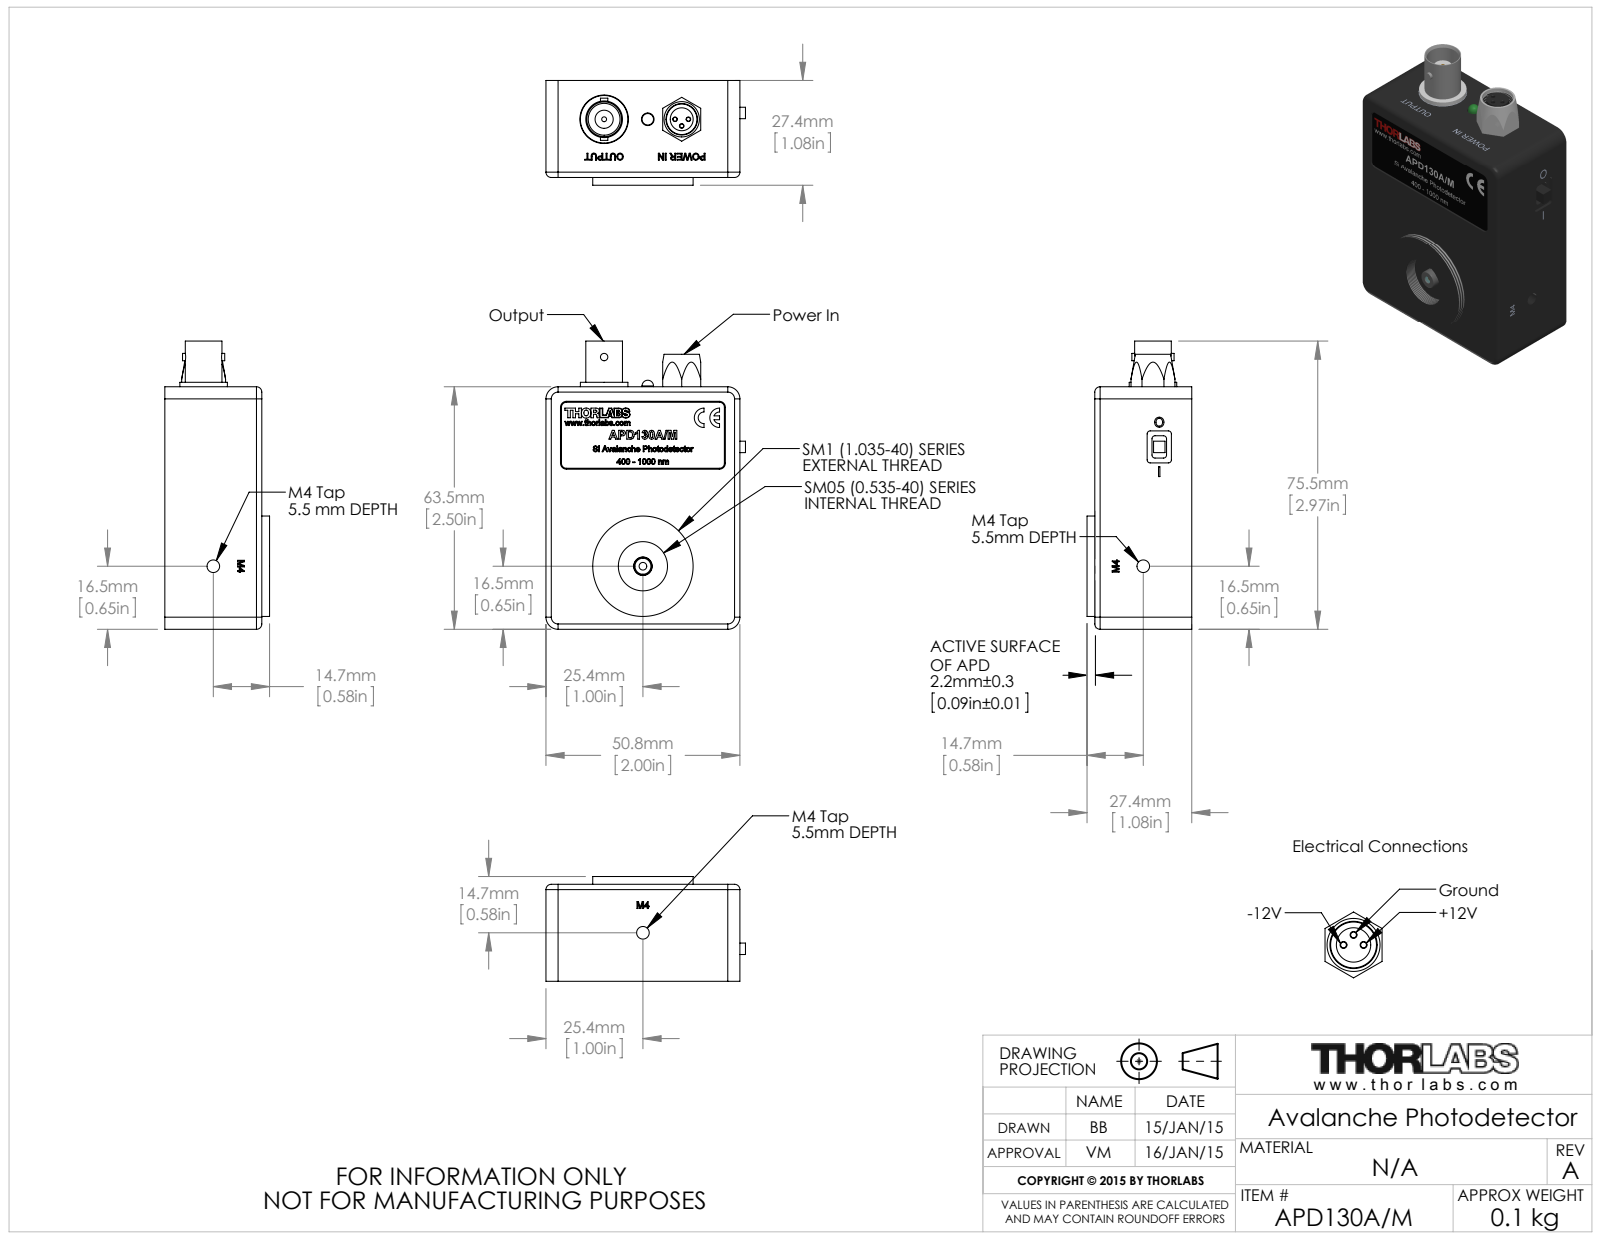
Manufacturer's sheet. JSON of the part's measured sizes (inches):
{"part_name": "MTN004760-E0W", "step_written_by": "SolidWorks 2014 (AUTOMOTIVE_DESIGN)", "units": "inches", "bodies": {"solids": 12, "faces": 1901, "planar": 1029, "cylindrical": 252, "other": 620}, "overall_size": [2.971, 2.057, 1.08], "volume_in3": 2.206, "surface_area_in2": 44.73, "round_holes": [[0.063, 8], [0.094, 4], [0.039, 3], [0.04, 3], [0.13, 2], [0.05, 1], [0.052, 1], [0.079, 1], [0.098, 1], [0.13, 1], [0.163, 1], [0.191, 1]], "round_bosses_or_shafts": [[0.02, 6], [0.15, 5], [0.079, 4], [0.018, 3], [1.035, 1], [0.49, 1], [0.43, 1], [0.378, 1]], "partial_cylinders_radius": [[0.125, 18], [0.13, 14], [0.031, 8], [0.075, 8], [0.095, 8], [0.1, 5], [0.05, 4], [0.055, 4]], "face_to_face_distances": [0.063, 0.1, 1, 0.937, 0.045, 0.02, 0.98, 0.917, 0.872, 0.935], "hole_center_spacings": [0.174, 1.621, 2.013, 2.579, 0.05, 0.069, 0.071, 0.097]}
